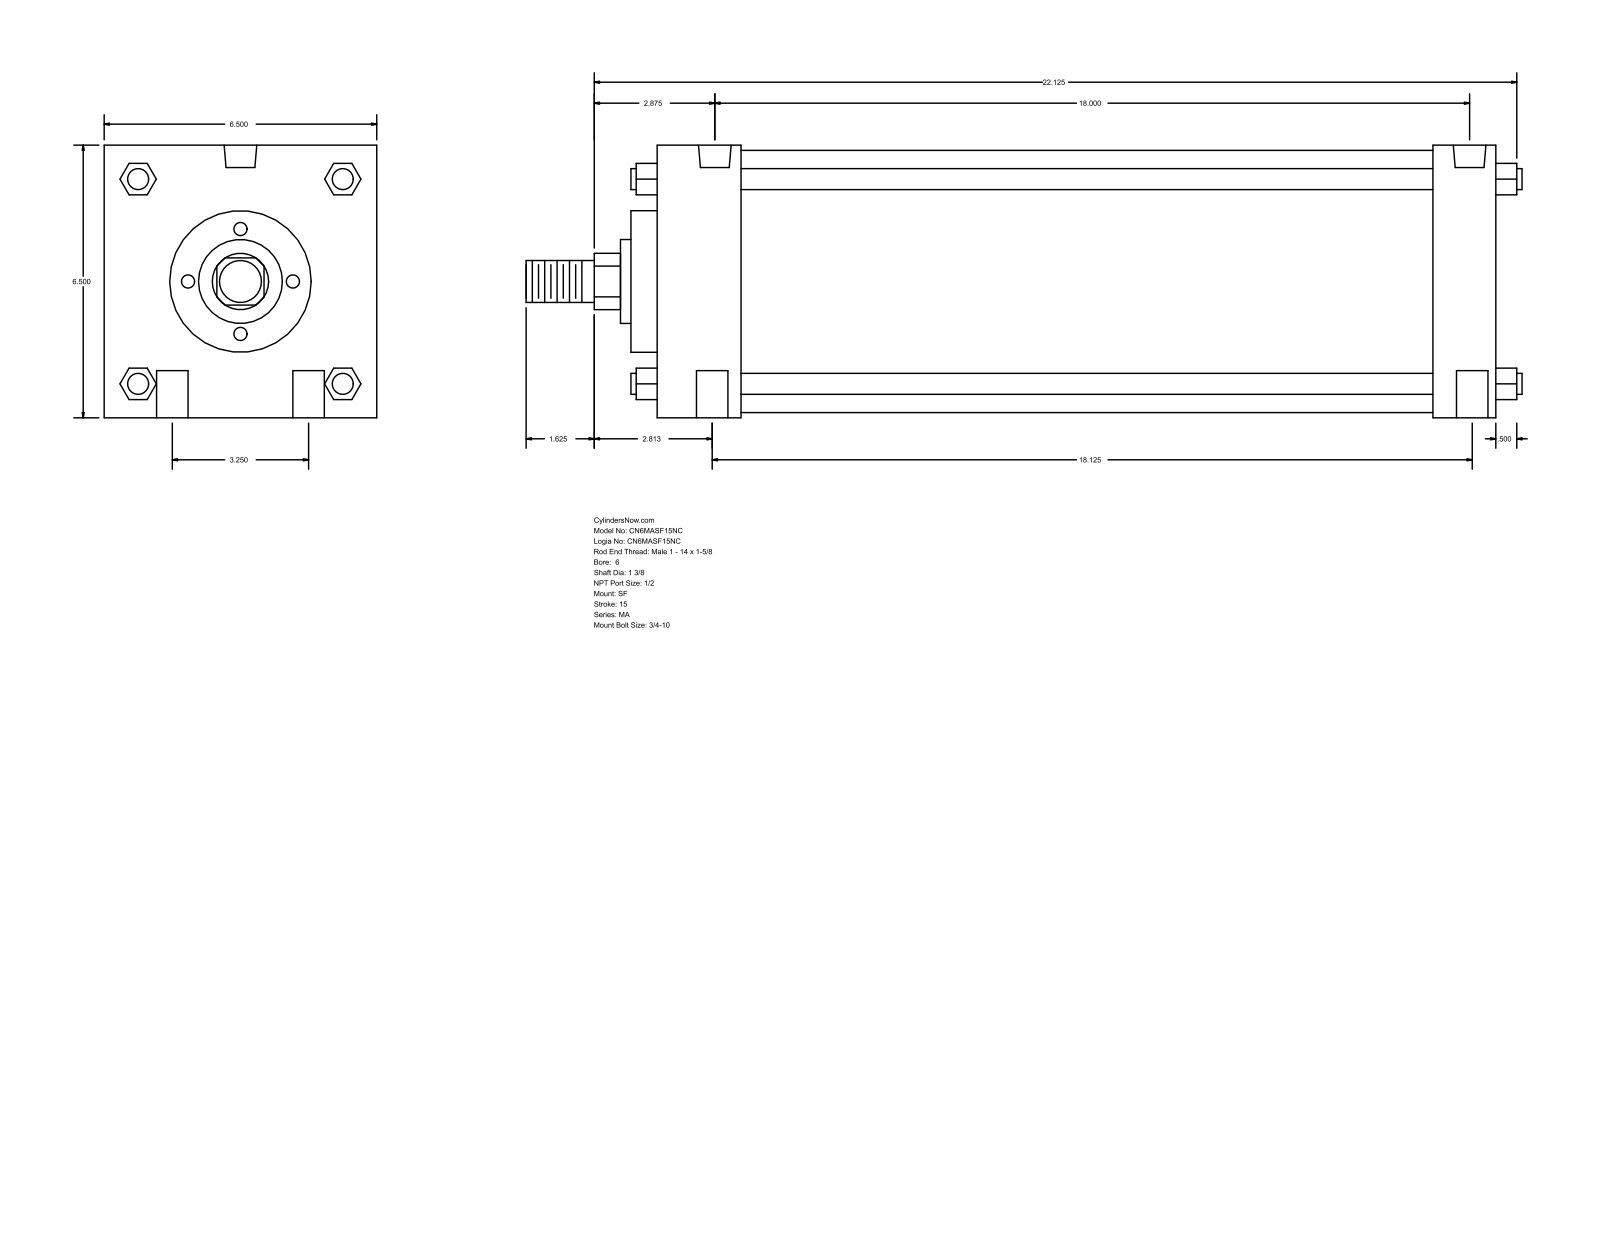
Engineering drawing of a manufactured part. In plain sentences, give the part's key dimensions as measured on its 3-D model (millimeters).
The part is named "MA_SF__0600_1.375". Its 3-D file was written by "GSSL Pune (CONFIG_CONTROL_DESIGN)". It is 0 solids with 126 faces: 95 planar, 31 cylindrical and 0 other. Overall it measures 603.25 by 165.1 by 165.1 millimeters. Round holes: 4 of diameter 19.05, 2 of diameter 17.46, 2 of diameter 19.77. Round bosses or shafts: 4 of diameter 12.7, 1 of diameter 158.75, 1 of diameter 85.72, 1 of diameter 50.8, 1 of diameter 34.92, 1 of diameter 25.4. Partial cylindrical surfaces (rounded edges, fillets, slot ends): 1 of radius 17.06. The main face-to-face distances are 165.1, 508, 469.9, 50.8, 38.1, 419.1, 457.2, 66.67, 15.87, 485.77. The hole center spacings are 41.3, 82.54, 457.2, 460.37, 460.63, 460.64, 467.71.
